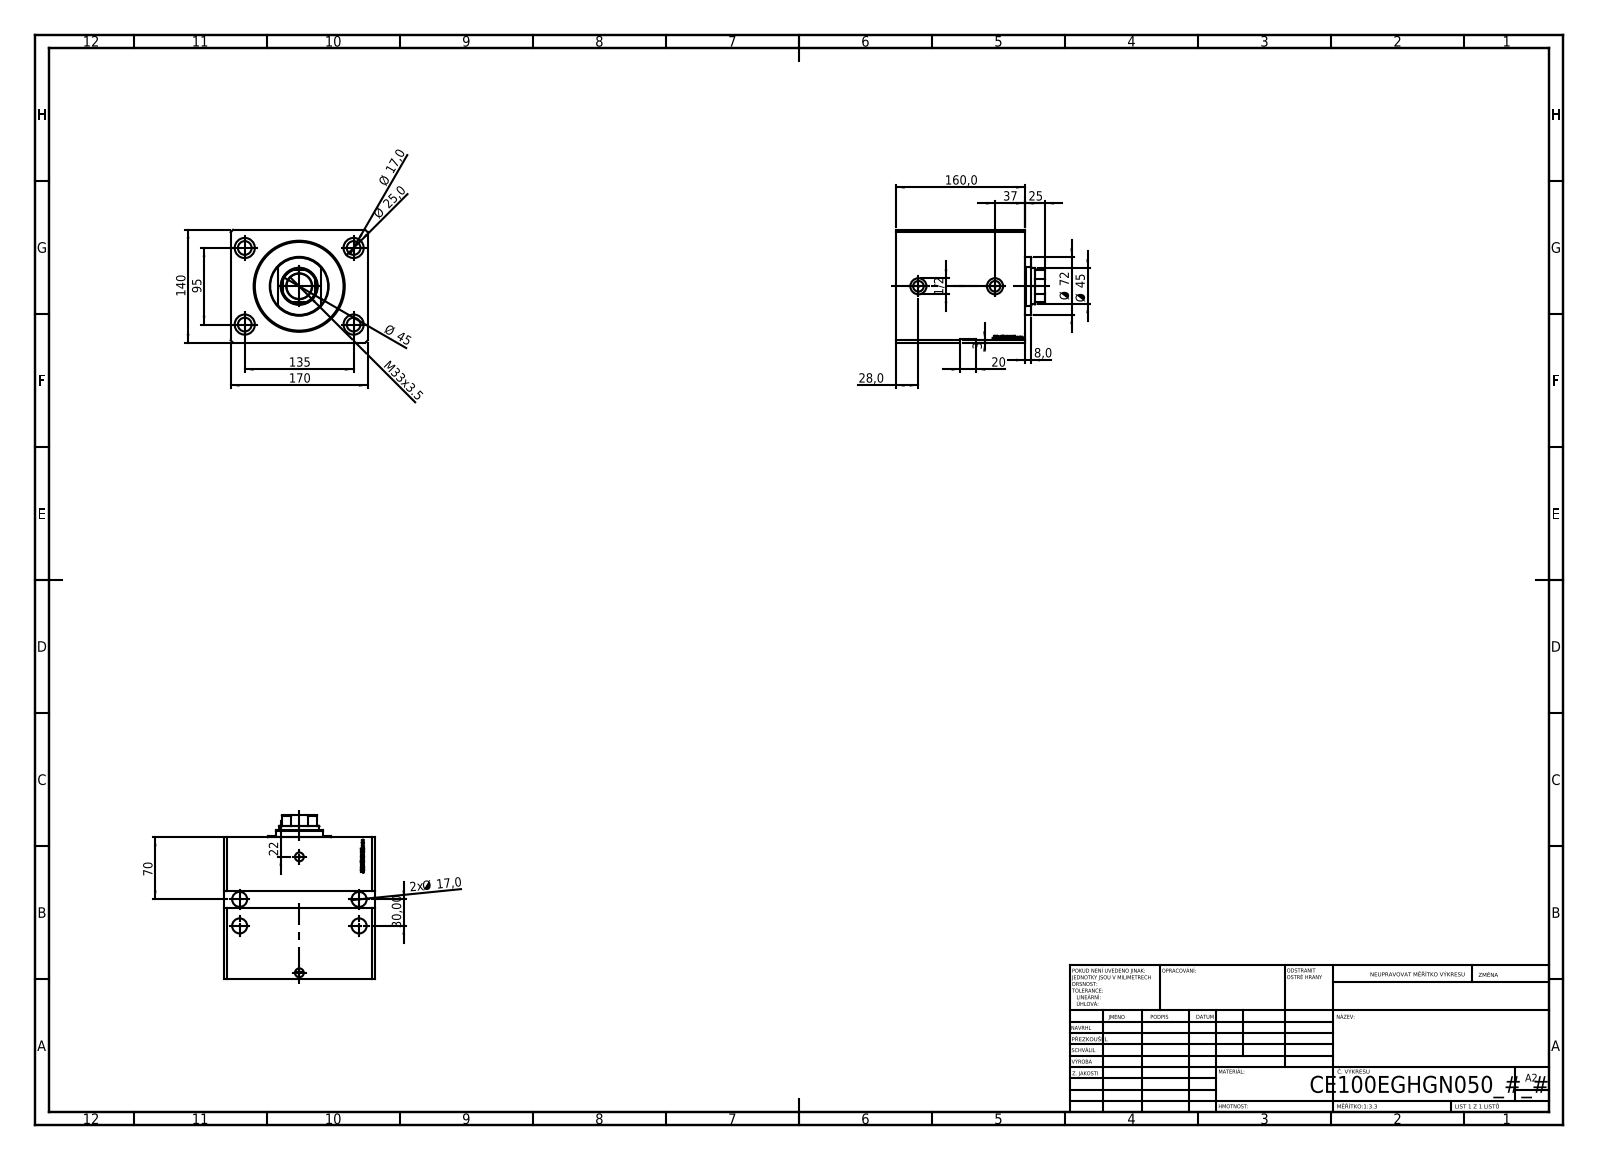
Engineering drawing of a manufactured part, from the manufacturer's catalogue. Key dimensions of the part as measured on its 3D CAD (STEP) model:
Part name (STEP PRODUCT): V250CE_E_Body; V250CE_C_VCP; V250CE_VC_E
STEP written by: SolidWorks 2019 (CONFIG_CONTROL_DESIGN)
Units: millimetres
Bodies: 3 solids, 953 faces (471 planar, 96 cylindrical, 386 other)
Overall size (bounding box): 185 × 170 × 140
Volume: 3 212 000 mm³ · Surface area: 328 709 mm²
Round holes (diameter × count): ⌀17 ×8, ⌀1.25 ×4, ⌀25 ×4, ⌀10 ×2, ⌀13.16 ×2, ⌀20 ×2, ⌀31.5 ×1, ⌀45 ×1, ⌀100 ×1, ⌀113 ×1
Round bosses / shafts (diameter × count): ⌀72 ×1
Partial cylindrical surfaces — rounded edges, fillets, slot ends (radius × count): R22 ×1
Main face-to-face distances: 140, 170, 160, 28.9, 131.1, 135, 25, 106.1, 50, 85
Hole centre spacings: 82.54, 135, 95, 30, 82.83, 85.49, 85.82, 103.15
